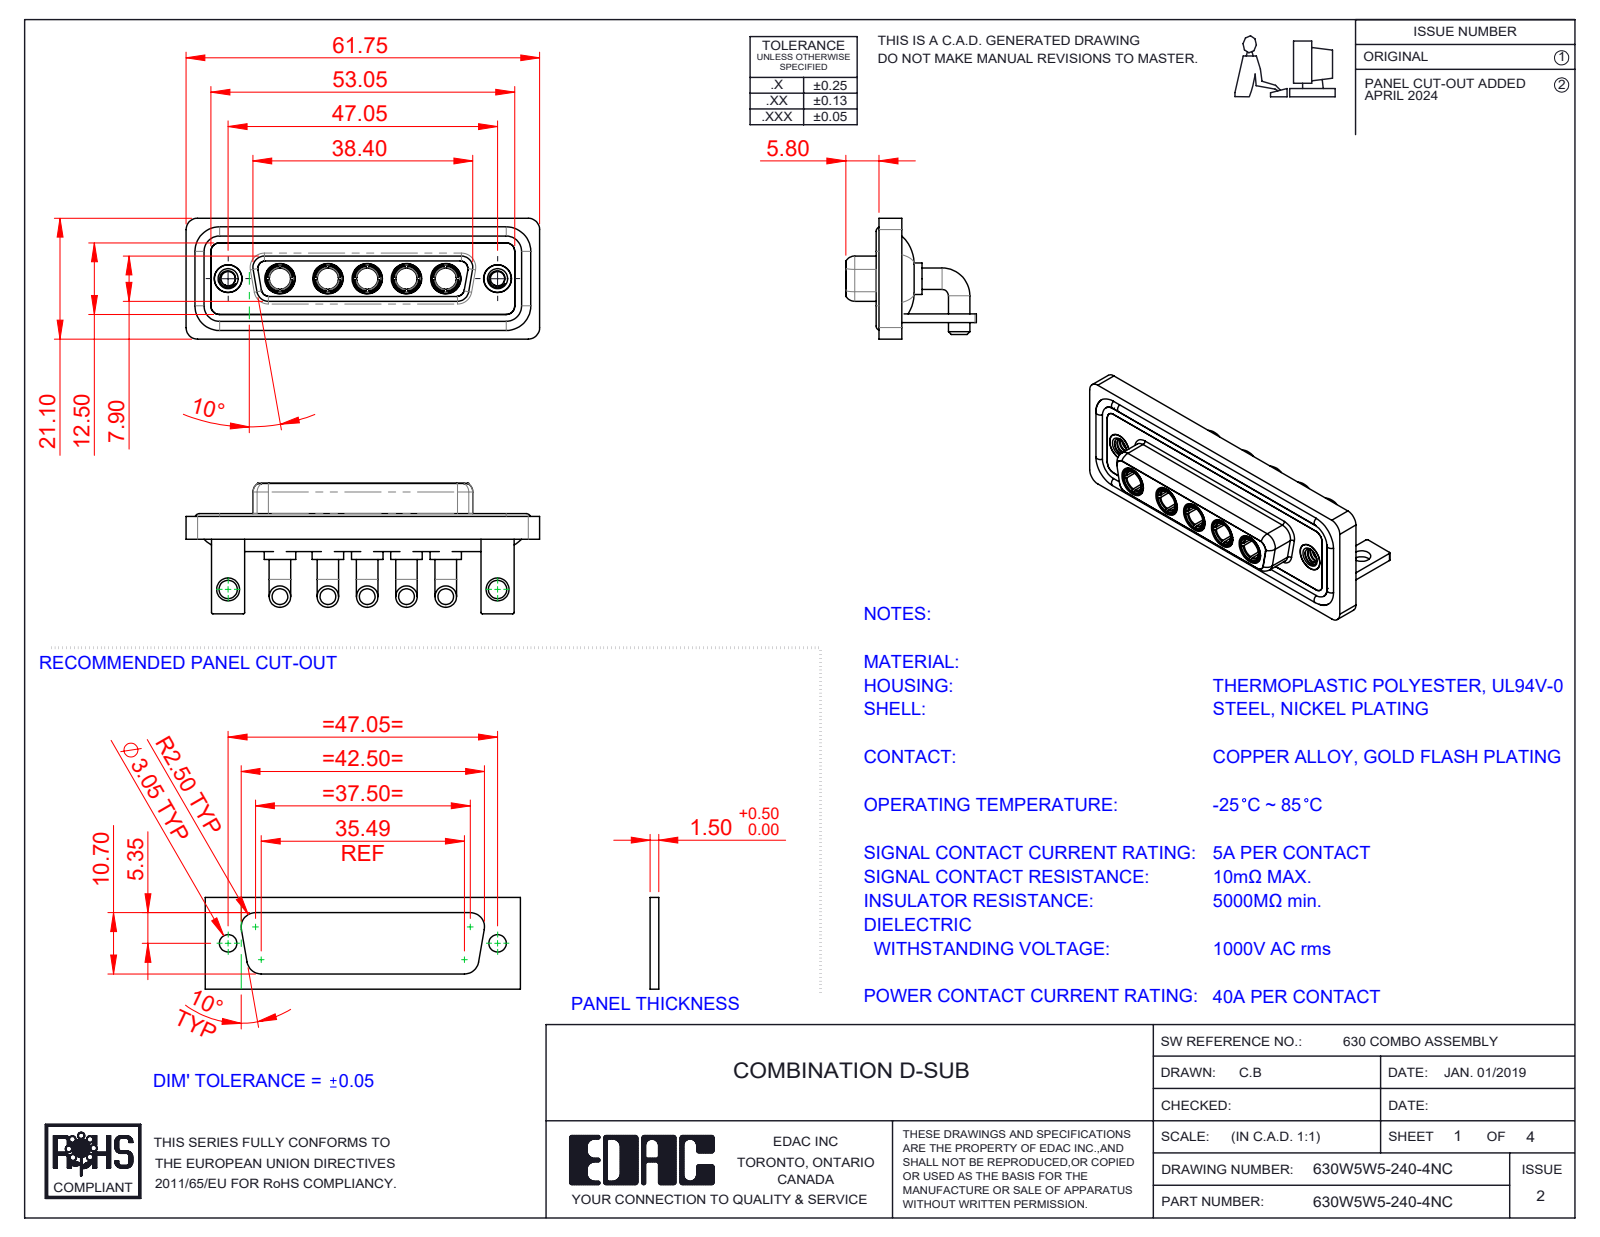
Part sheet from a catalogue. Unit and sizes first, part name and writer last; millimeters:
Units: millimetres
Overall size (bounding box): 61.75 × 22.8 × 21.1
Round holes (diameter × count): ⌀4.85 ×7, ⌀3.7 ×5, ⌀5.3 ×5, ⌀2.5 ×2, ⌀3.2 ×2, ⌀4 ×2, ⌀4.05 ×2, ⌀5 ×2
Round bosses / shafts (diameter × count): ⌀3.75 ×10, ⌀5.5 ×5, ⌀5.2 ×5, ⌀4.96 ×5, ⌀4.75 ×5, ⌀1.6 ×4, ⌀4.95 ×2, ⌀4.8 ×2
Partial cylindrical surfaces — rounded edges, fillets, slot ends (radius × count): R2 ×19, R1.5 ×18, R0.25 ×16, R1.35 ×8, R1.6 ×8, R0.5 ×5, R2.1 ×5, R0.6 ×4
Main face-to-face distances: 0.4, 1.8, 2.9, 3.7, 1.5, 4.1, 1.1, 1.4, 1.6, 2.5
Hole centre spacings: 6.86, 9.04, 38.01, 47.05, 6.87, 8.38, 13.72, 13.73
Volume: 9 158 mm³ · Surface area: 14 771 mm²
Bodies: 19 solids, 818 faces (270 planar, 335 cylindrical, 213 other)
Part name (STEP PRODUCT): 630W5W5-240-4NC; 630Combo Stabilizer Bracket_50 Contacts; 630Combo Shell Rear_25 Contacts; 630Combo Housing_5W5 (+4 more)
STEP written by: SolidWorks 2023 (CONFIG_CONTROL_DESIGN)
